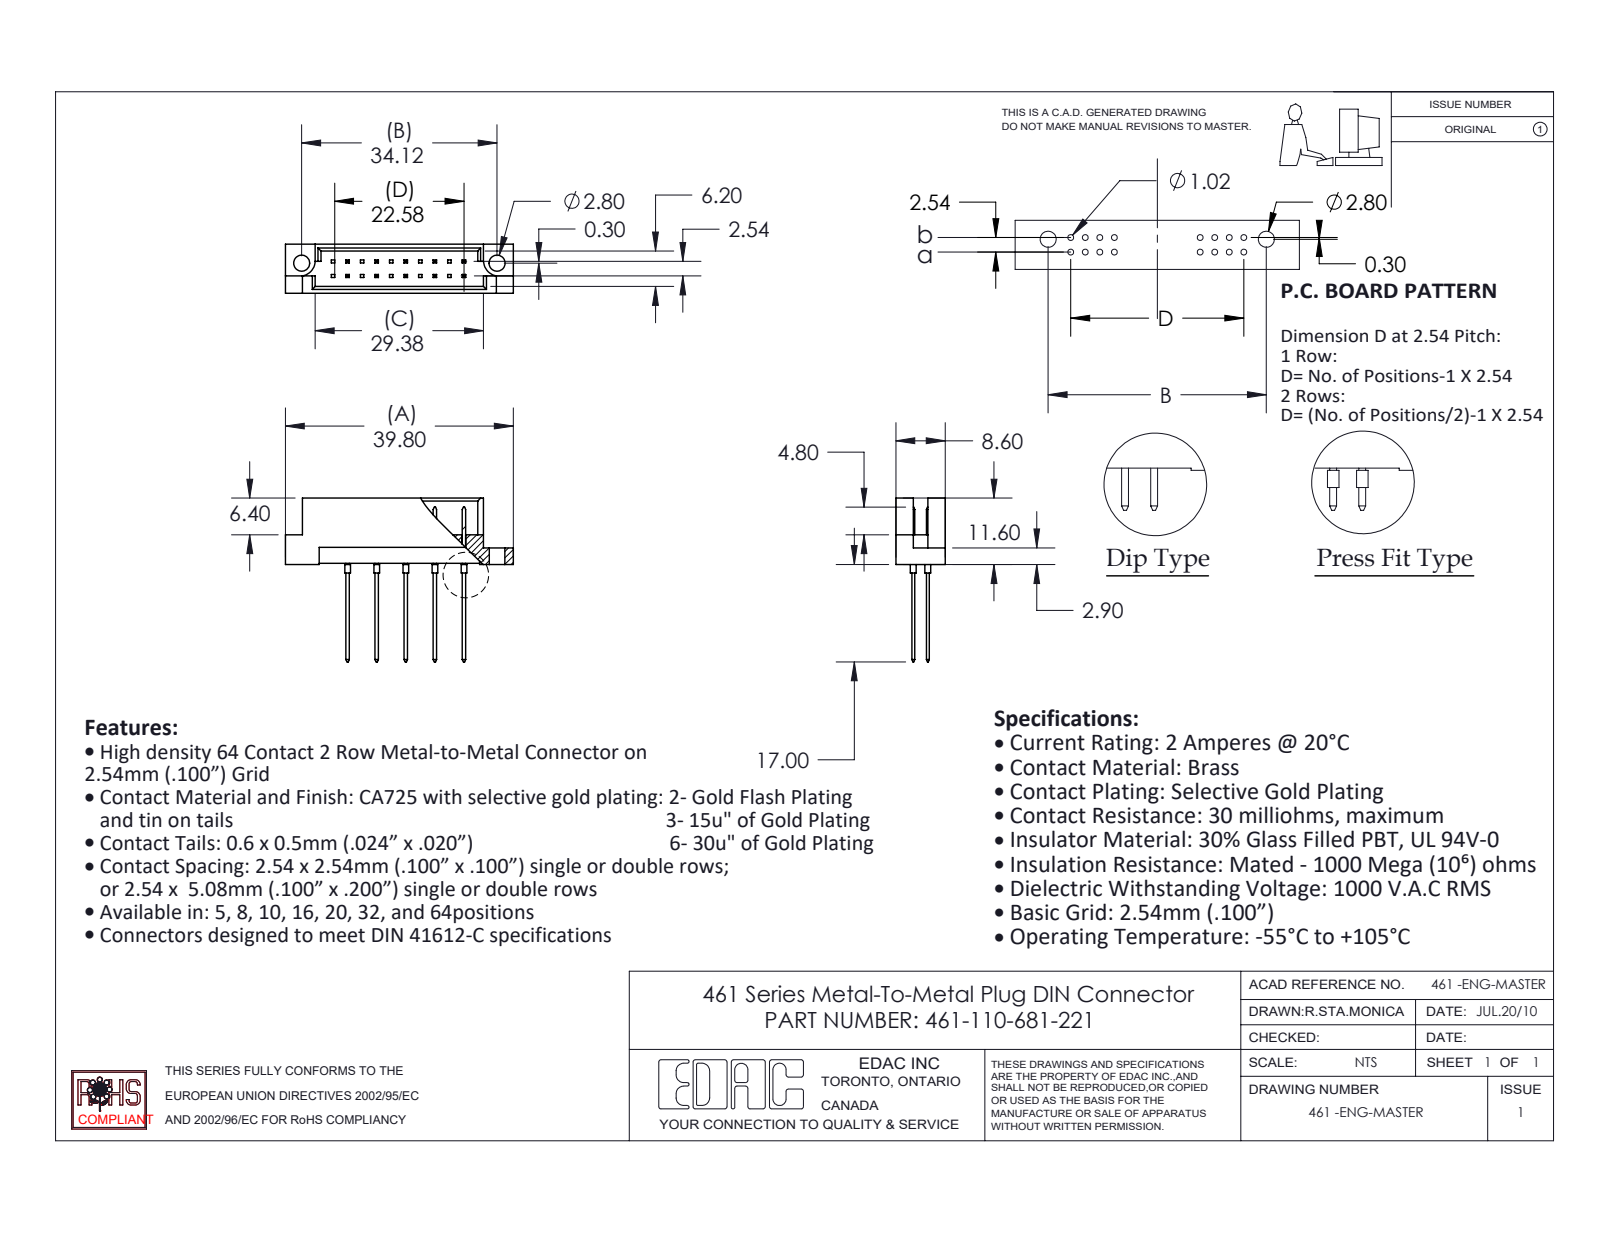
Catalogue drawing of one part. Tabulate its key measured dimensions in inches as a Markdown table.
| quantity | value |
| --- | --- |
| part name | 461-290_81; 461 Part_20; 461-110-681-221 |
| STEP written by | SolidWorks 2020 (CONFIG_CONTROL_DESIGN) |
| units | inches |
| bodies | 11 solids, 348 faces (322 planar, 26 cylindrical, 0 other) |
| overall size | 1.567 × 1.126 × 0.339 |
| volume | 0.122 in³ |
| surface area | 4.576 in² |
| round holes (diameter × count) | 0.11 × 2 |
| round bosses / shafts (diameter × count) | 0.039 × 10 |
| partial cylindrical surfaces (radius × count) | 0.11 × 2 |
| main face-to-face distances | 0.047, 0.291, 0.339, 0.244, 0.2, 0.1, 0.109, 0.129, 0.209, 0.229 |
| hole center spacings | 1.343 |
